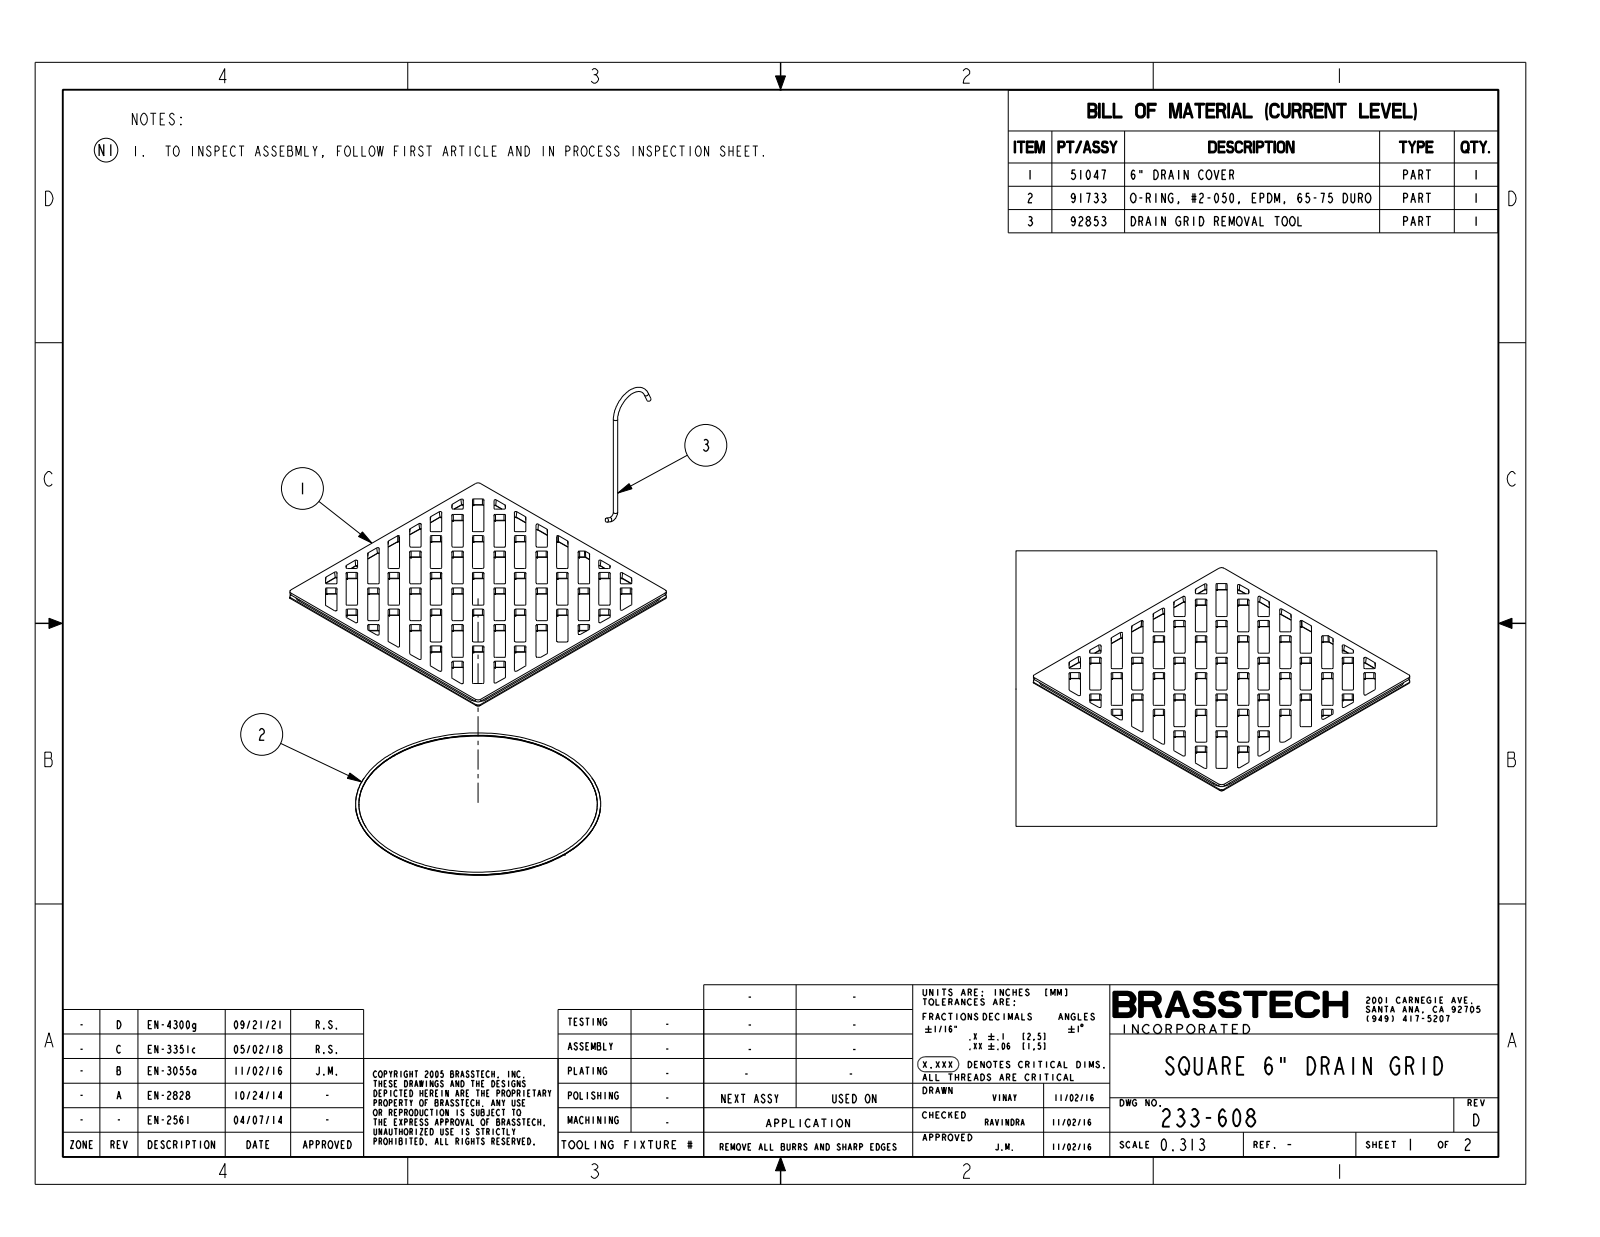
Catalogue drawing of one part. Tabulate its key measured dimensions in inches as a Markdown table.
| quantity | value |
| --- | --- |
| part name | 51047 |
| STEP written by | CREO PARAMETRIC BY PTC INC, 2018400 (AUTOMOTIVE_DESIGN) |
| units | inches |
| bodies | 1 solid, 960 faces (252 planar, 302 cylindrical, 406 other) |
| overall size | 5.895 × 5.895 × 0.188 |
| volume | 3.515 in³ |
| surface area | 70.85 in² |
| partial cylindrical surfaces (radius × count) | 0.02 × 179, 0.03 × 58, 0.08 × 4, 0.25 × 4 |
| main face-to-face distances | 0.188, 0.921, 1.842, 0.448, 0.473, 1.394, 2.763, 1.369, 2.29, 2.315 |
